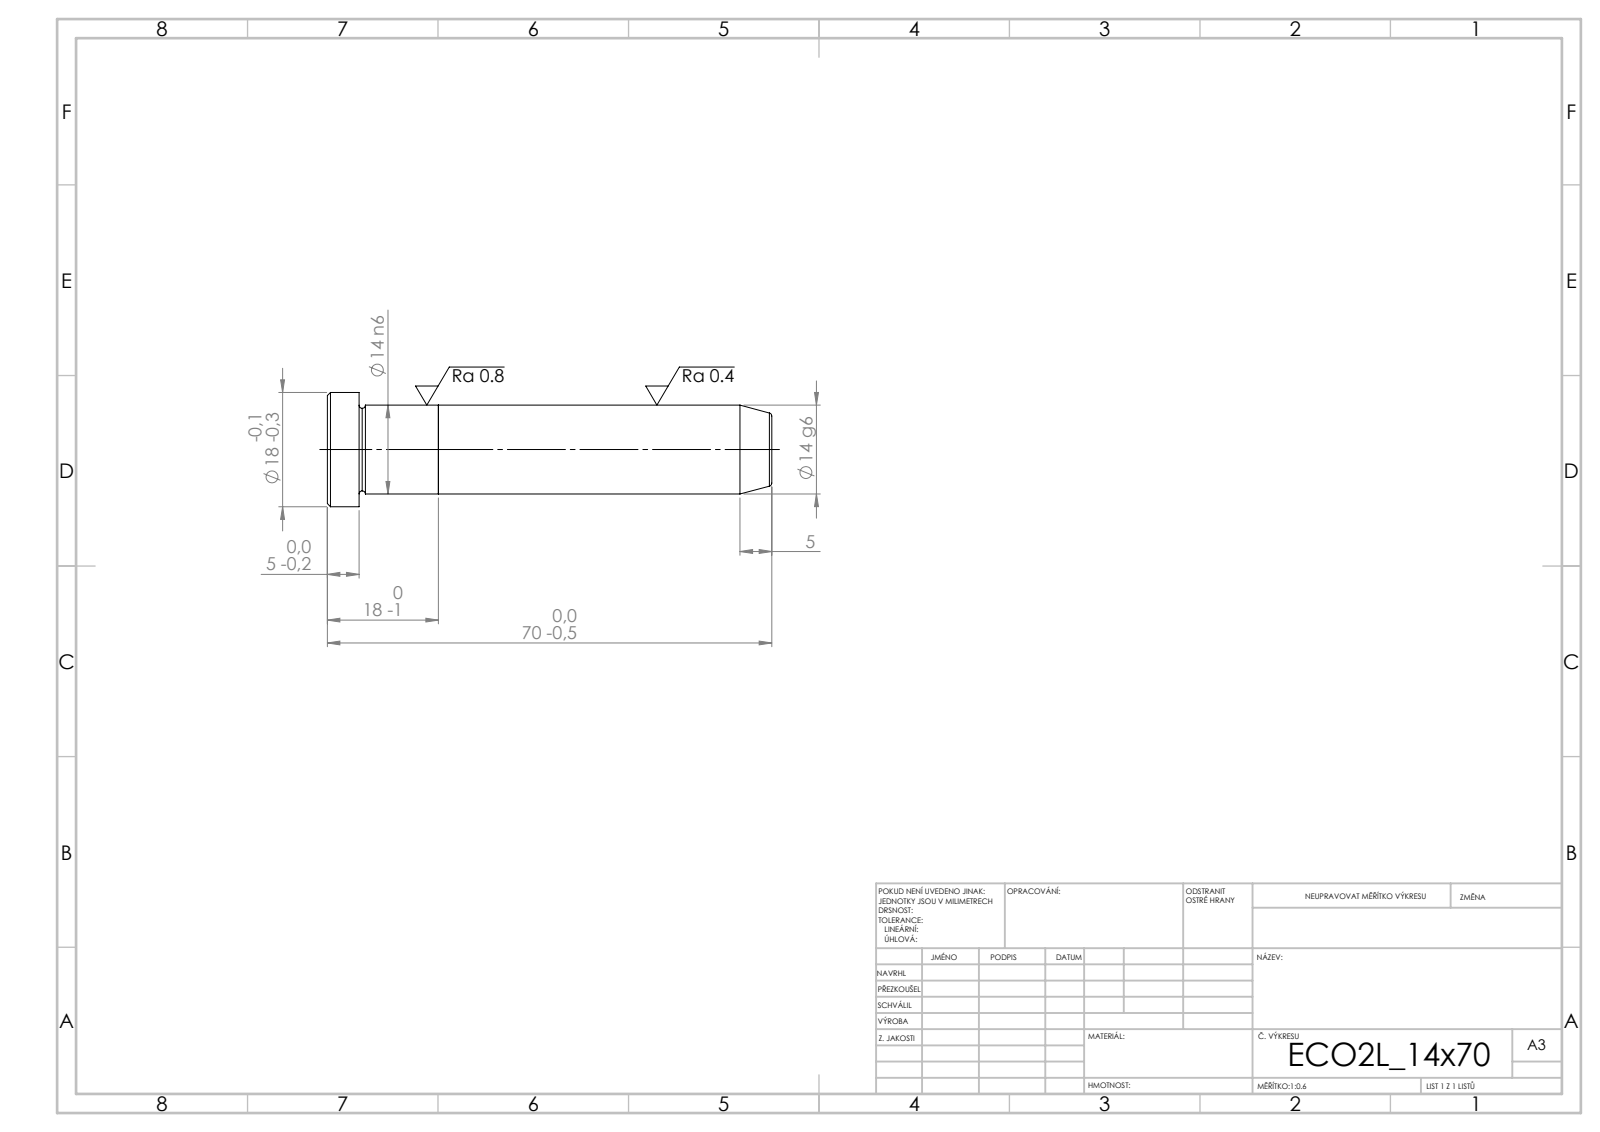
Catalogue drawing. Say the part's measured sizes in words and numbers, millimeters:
Its 3-D file was written by "SolidWorks 2019 (CONFIG_CONTROL_DESIGN)". It is 2 solids with 21 faces: 5 planar, 6 cylindrical and 10 other. Overall it measures 70 by 18 by 18 millimeters. Its volume is 11 116 cubic millimeters and its surface area 3 892 square millimeters. Round bosses or shafts: 1 of diameter 18, 1 of diameter 14. The main face-to-face distances are 17.5, 12.5, 5, 52.5, 65, 70.
